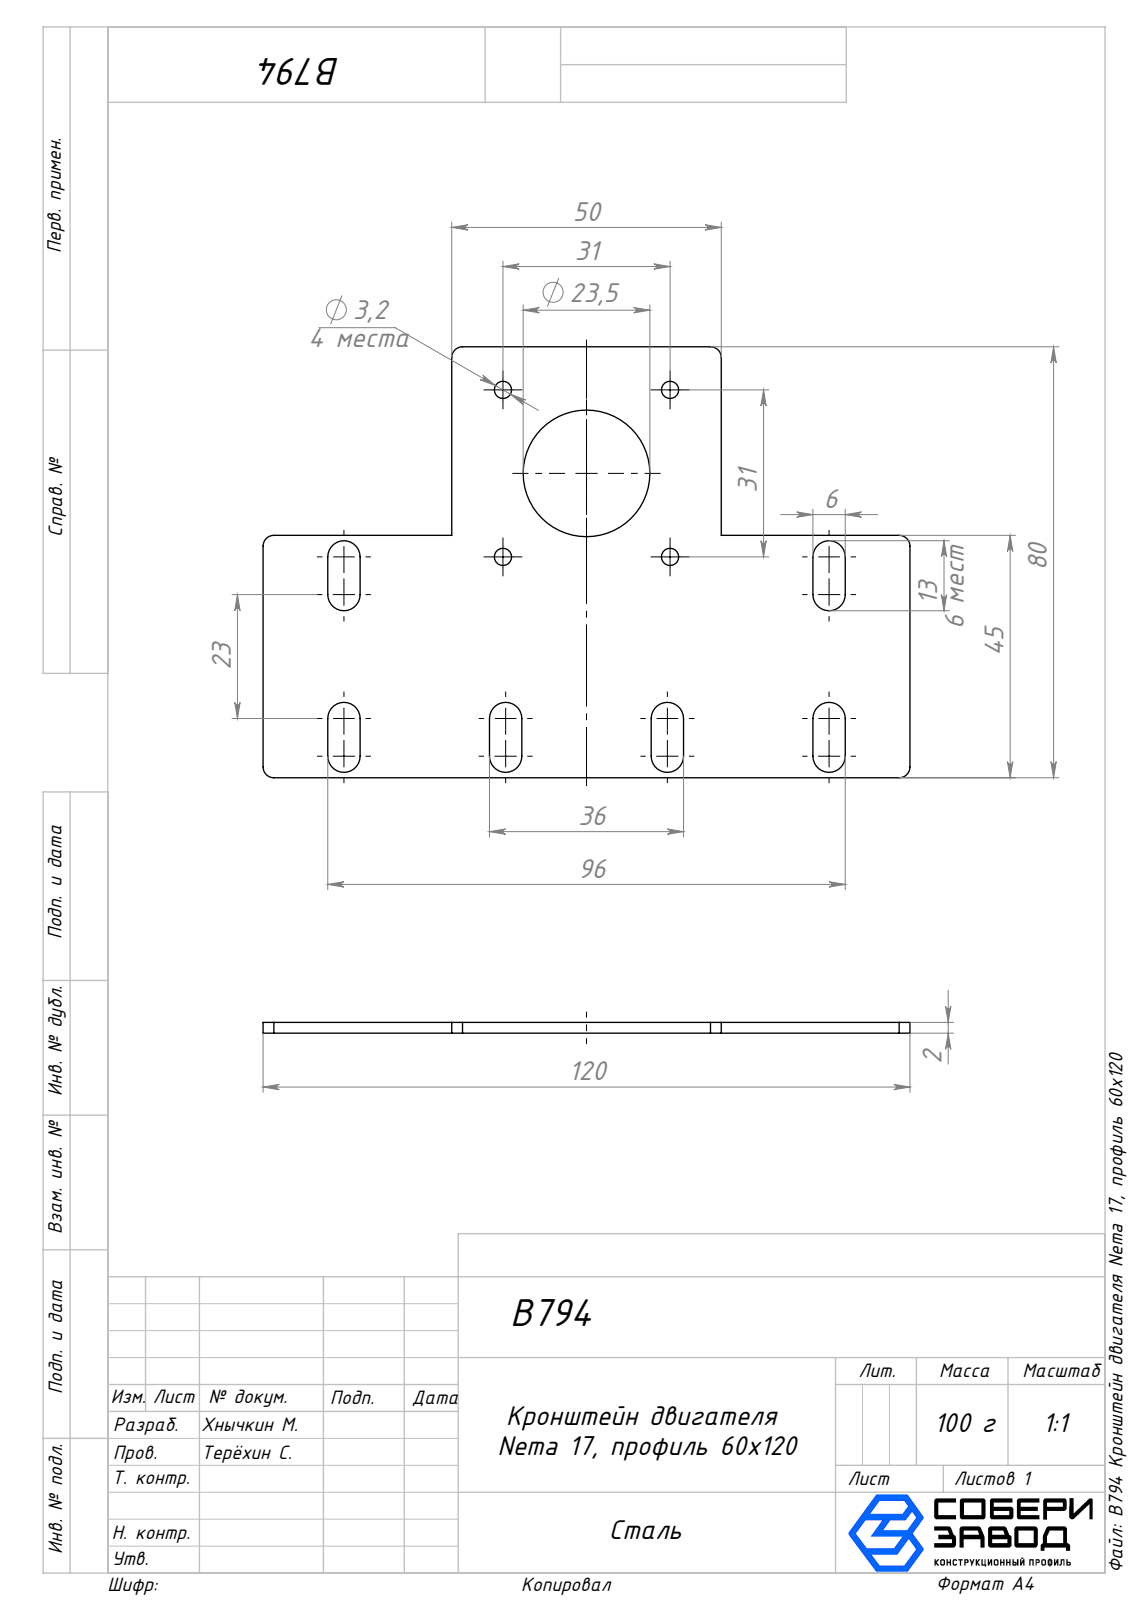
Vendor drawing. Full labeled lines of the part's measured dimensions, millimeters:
Part name (STEP PRODUCT): B794 Кронштейн двигателя Nema 17, профиль 60х120
STEP written by: SolidWorks 2025 (AUTOMOTIVE_DESIGN)
Units: millimetres
Bodies: 1 solid, 50 faces (22 planar, 28 cylindrical, 0 other)
Overall size (bounding box): 120 × 80 × 2
Volume: 12 515 mm³ · Surface area: 13 927 mm²
Round holes (diameter × count): ⌀3.2 ×4, ⌀23.5 ×1
Partial cylindrical surfaces — rounded edges, fillets, slot ends (radius × count): R3 ×12, R2 ×6
Main face-to-face distances: 2, 35, 85, 45, 80, 30, 6, 120, 50, 12
Hole centre spacings: 21.92, 31, 43.84
